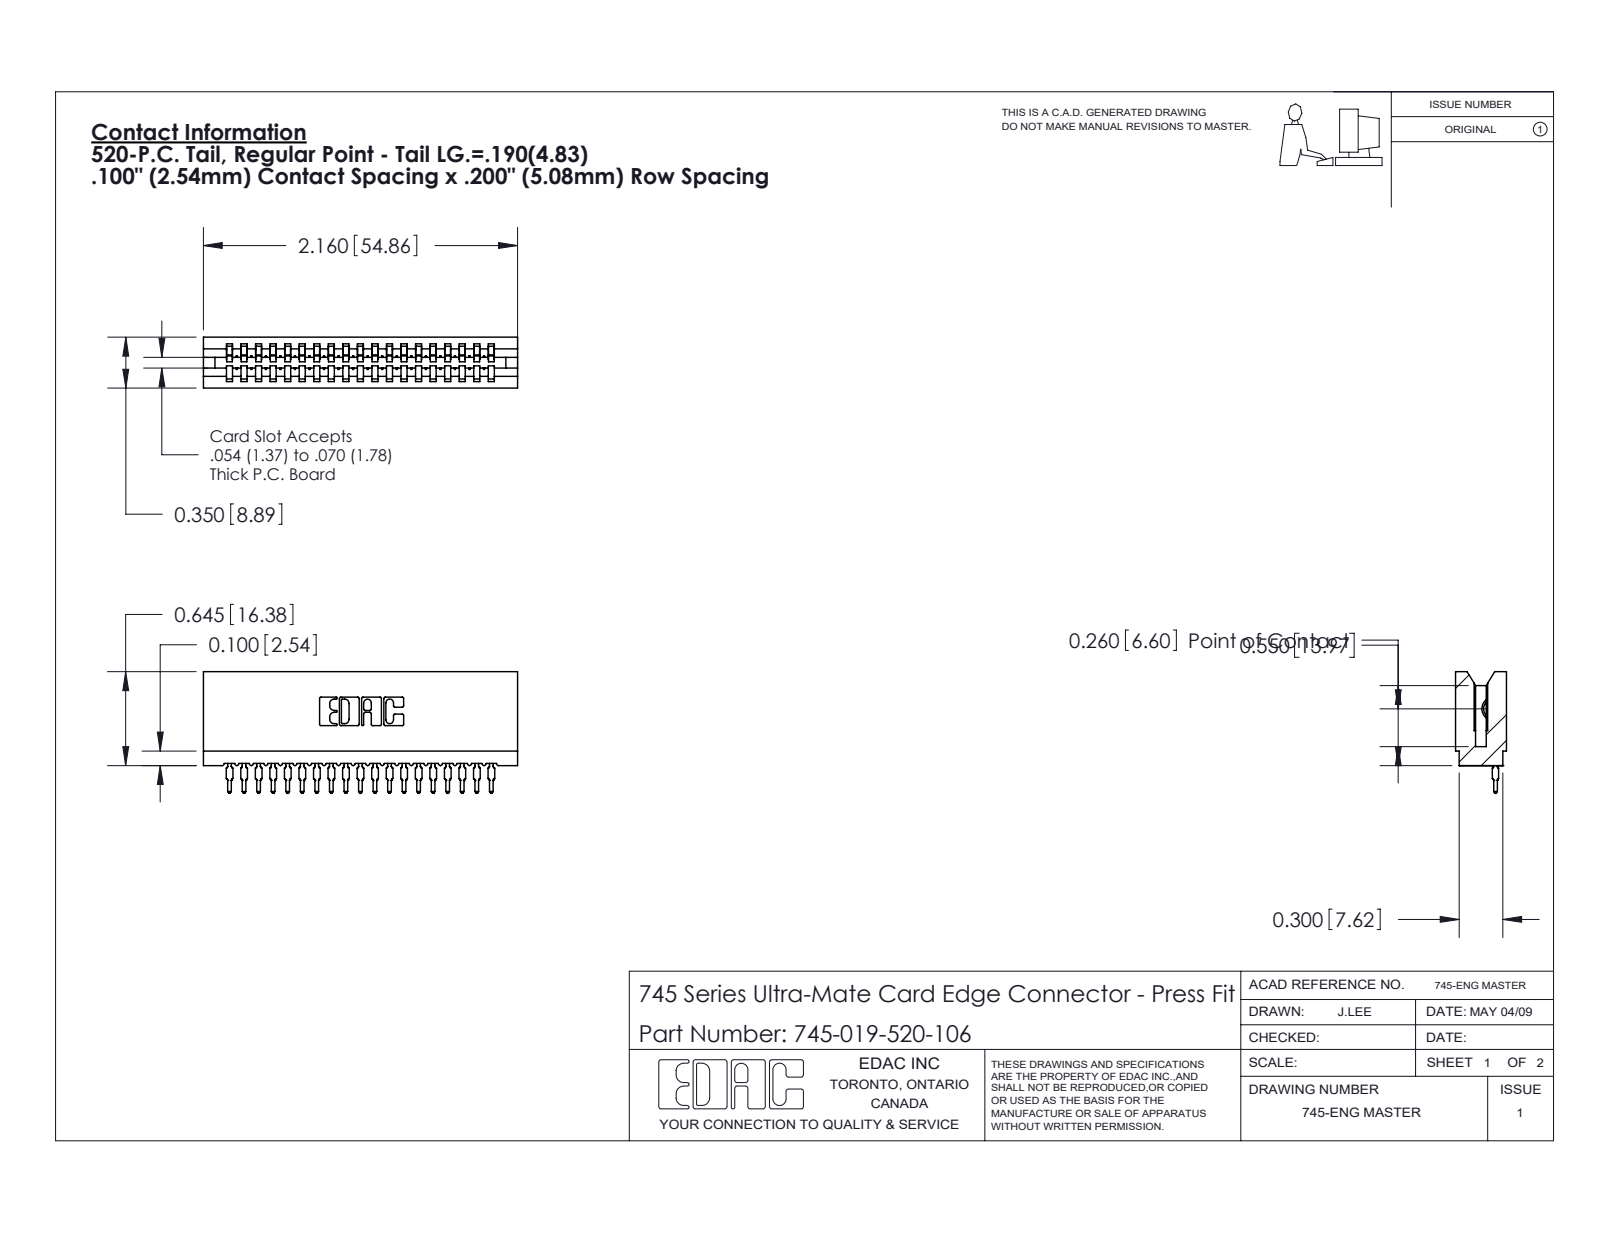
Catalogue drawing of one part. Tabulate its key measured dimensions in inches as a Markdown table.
| quantity | value |
| --- | --- |
| part name | 745-019-520-106; 745 Part_Insulator Option - 06; 745-292-001_520 |
| STEP written by | SolidWorks 2020 (CONFIG_CONTROL_DESIGN) |
| units | inches |
| bodies | 20 solids, 2224 faces (1329 planar, 401 cylindrical, 494 other) |
| overall size | 2.16 × 0.836 × 0.35 |
| volume | 0.296 in³ |
| surface area | 13.18 in² |
| partial cylindrical surfaces (radius × count) | 0.015 × 38, 0.021 × 38, 0.01 × 22, 0.007 × 6, 0.031 × 6, 0.005 × 4, 0.011 × 4, 0.026 × 3 |
| main face-to-face distances | 0.1, 0.2, 0.35, 0.5, 0.4, 0.138, 0.212, 0.6, 0.3, 0.045 |
